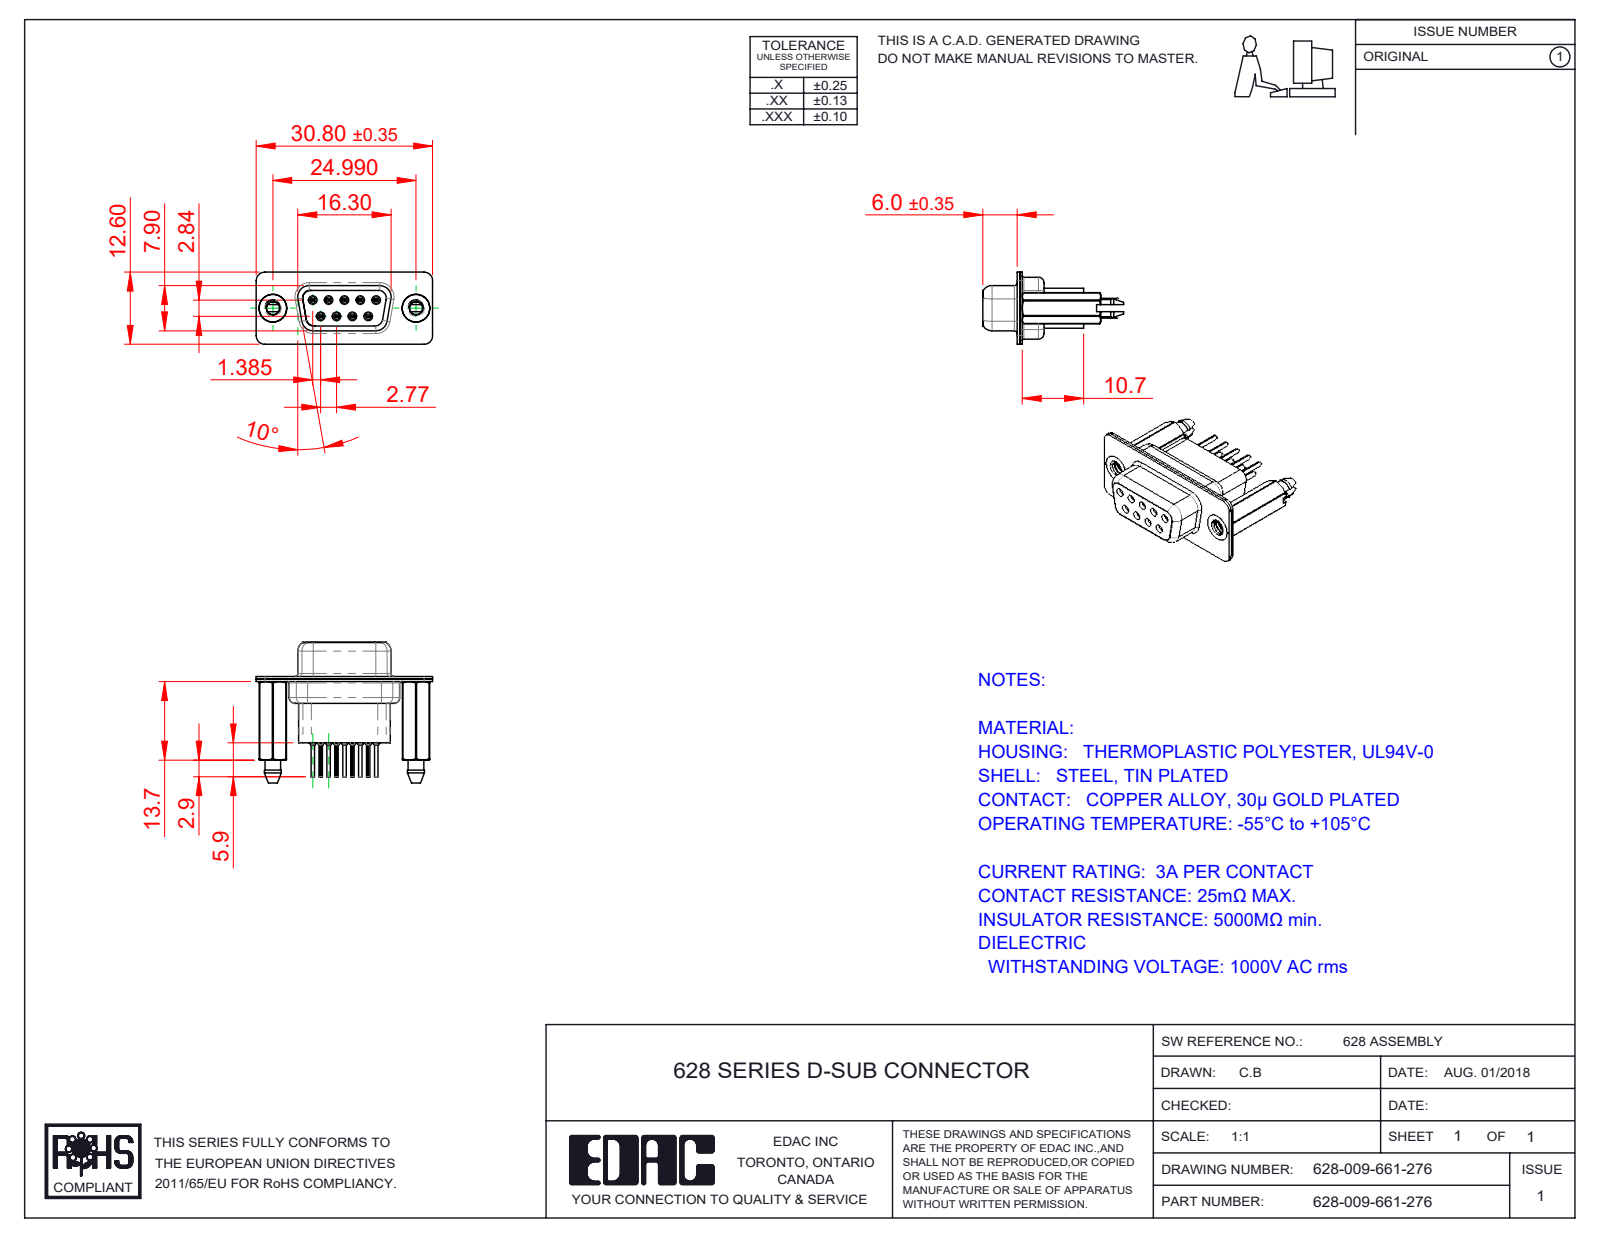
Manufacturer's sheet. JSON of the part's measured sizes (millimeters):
{"part_name": "628 Housing_09 HP; 628 4-40 Threaded Boardlock_HP61; 628 Shell Rear_09 Contacts; 628-009-661-276 (+3 more)", "step_written_by": "SolidWorks 2020 (CONFIG_CONTROL_DESIGN)", "units": "millimeters", "bodies": {"solids": 14, "faces": 1460, "planar": 378, "cylindrical": 466, "other": 616}, "overall_size": [30.8, 24.6, 12.6], "volume_mm3": 2591, "surface_area_mm2": 6029, "round_holes": [[0.2, 9], [0.8, 9], [0.9, 9], [1.1, 9], [1.6, 9], [1.7, 5], [2.26, 2], [4, 2], [4.05, 2], [4.85, 2]], "round_bosses_or_shafts": [[2, 9], [1.5, 9], [1.2, 9], [0.6, 9], [4.95, 2], [4.8, 2]], "partial_cylinders_radius": [[1.5, 19], [0.1, 18], [2, 12], [0.28, 9], [1.35, 6], [1.6, 6], [0.25, 4], [0.5, 4]], "face_to_face_distances": [0.45, 0.4, 0.9, 8.5, 6.6, 1.9, 1.4, 4.76, 7, 10.7], "hole_center_spacings": [3.16, 2.77, 5.54, 5.03, 5.04, 8.31, 7.48, 7.49]}
